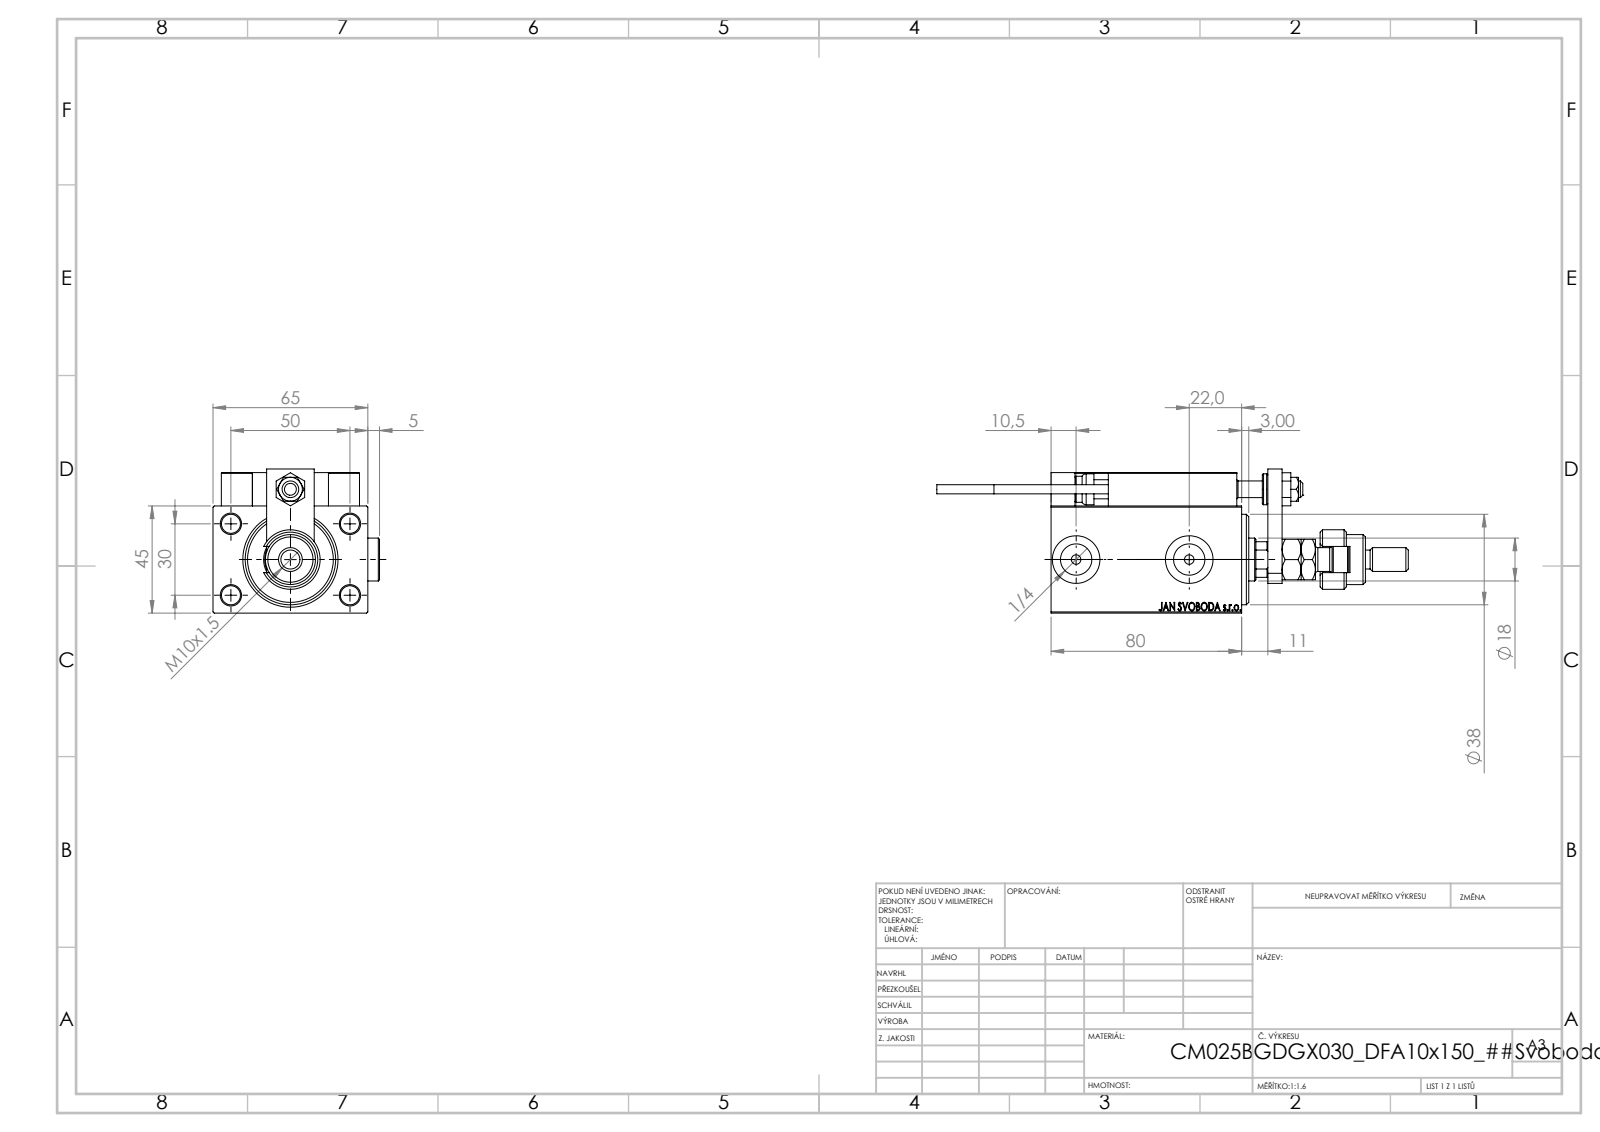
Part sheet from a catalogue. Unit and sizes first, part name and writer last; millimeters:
Units: millimetres
Overall size (bounding box): 198 × 69.9 × 60.5
Round holes (diameter × count): ⌀8 ×9, ⌀4 ×6, ⌀3.2 ×4, ⌀5 ×2, ⌀13.16 ×2, ⌀20 ×2, ⌀7 ×1, ⌀8.5 ×1, ⌀14.5 ×1, ⌀18 ×1, ⌀21.5 ×1, ⌀22.5 ×1
Round bosses / shafts (diameter × count): ⌀18 ×2, ⌀5 ×2, ⌀3.8 ×2, ⌀25 ×1, ⌀21 ×1, ⌀16 ×1, ⌀13 ×1, ⌀11 ×1
Partial cylindrical surfaces — rounded edges, fillets, slot ends (radius × count): R0.3 ×30, R3 ×2, R5.5 ×1, R8.5 ×1, R8.75 ×1
Main face-to-face distances: 45, 14, 65, 59, 6, 5, 13, 91, 19, 3.5
Hole centre spacings: 29.15, 11.37, 20, 28.9, 29.59, 29.69, 30, 32.06
Volume: 276 677 mm³ · Surface area: 76 456 mm²
Bodies: 28 solids, 1457 faces (623 planar, 213 cylindrical, 621 other)
Part name (STEP PRODUCT): NUT_D10; TYC_L79; SWITCH DIM B,W; ALLEN BOLT D5 (+8 more)
STEP written by: SolidWorks 2019 (CONFIG_CONTROL_DESIGN)
